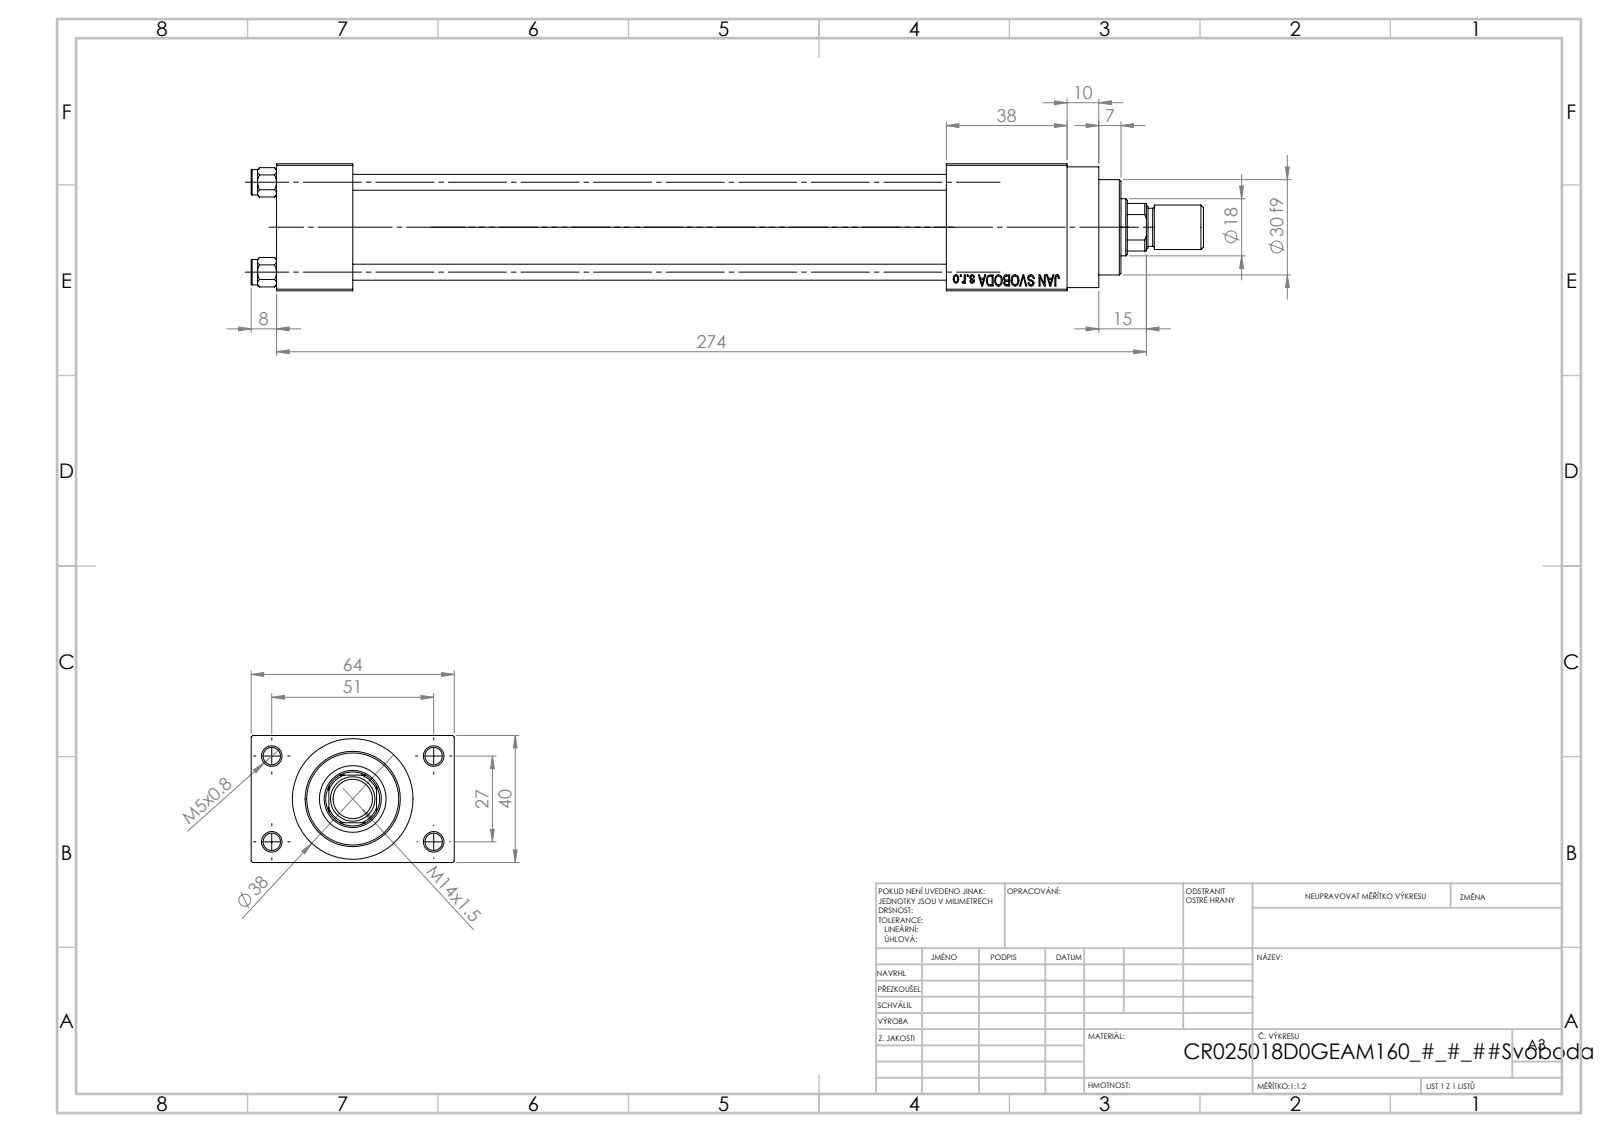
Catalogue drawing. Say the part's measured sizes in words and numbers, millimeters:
The part is named "V215CR_D_TYCINKA; V215CR_D_Body; NUT_M5_D; V215CR_VCP_D (+2 more)". Its 3-D file was written by "SolidWorks 2019 (CONFIG_CONTROL_DESIGN)". It is 12 solids with 1114 faces: 499 planar, 91 cylindrical and 524 other. Overall it measures 300 by 64 by 40 millimeters. Its volume is 267 032 cubic millimeters and its surface area 106 682 square millimeters. Round holes: 4 of diameter 5, 4 of diameter 5.5, 3 of diameter 20, 2 of diameter 7, 2 of diameter 13.16, 1 of diameter 8.5, 1 of diameter 18, 1 of diameter 21, 1 of diameter 25, 1 of diameter 30. Round bosses or shafts: 4 of diameter 8, 1 of diameter 38, 1 of diameter 31, 1 of diameter 14, 1 of diameter 12. Partial cylindrical surfaces (rounded edges, fillets, slot ends): 1 of radius 8.5. The main face-to-face distances are 40, 12, 52, 187, 24, 211, 64, 38, 249, 225. The hole center spacings are 11.37, 20.01, 28.3, 28.85, 29.89, 39.66, 48.34, 27.
